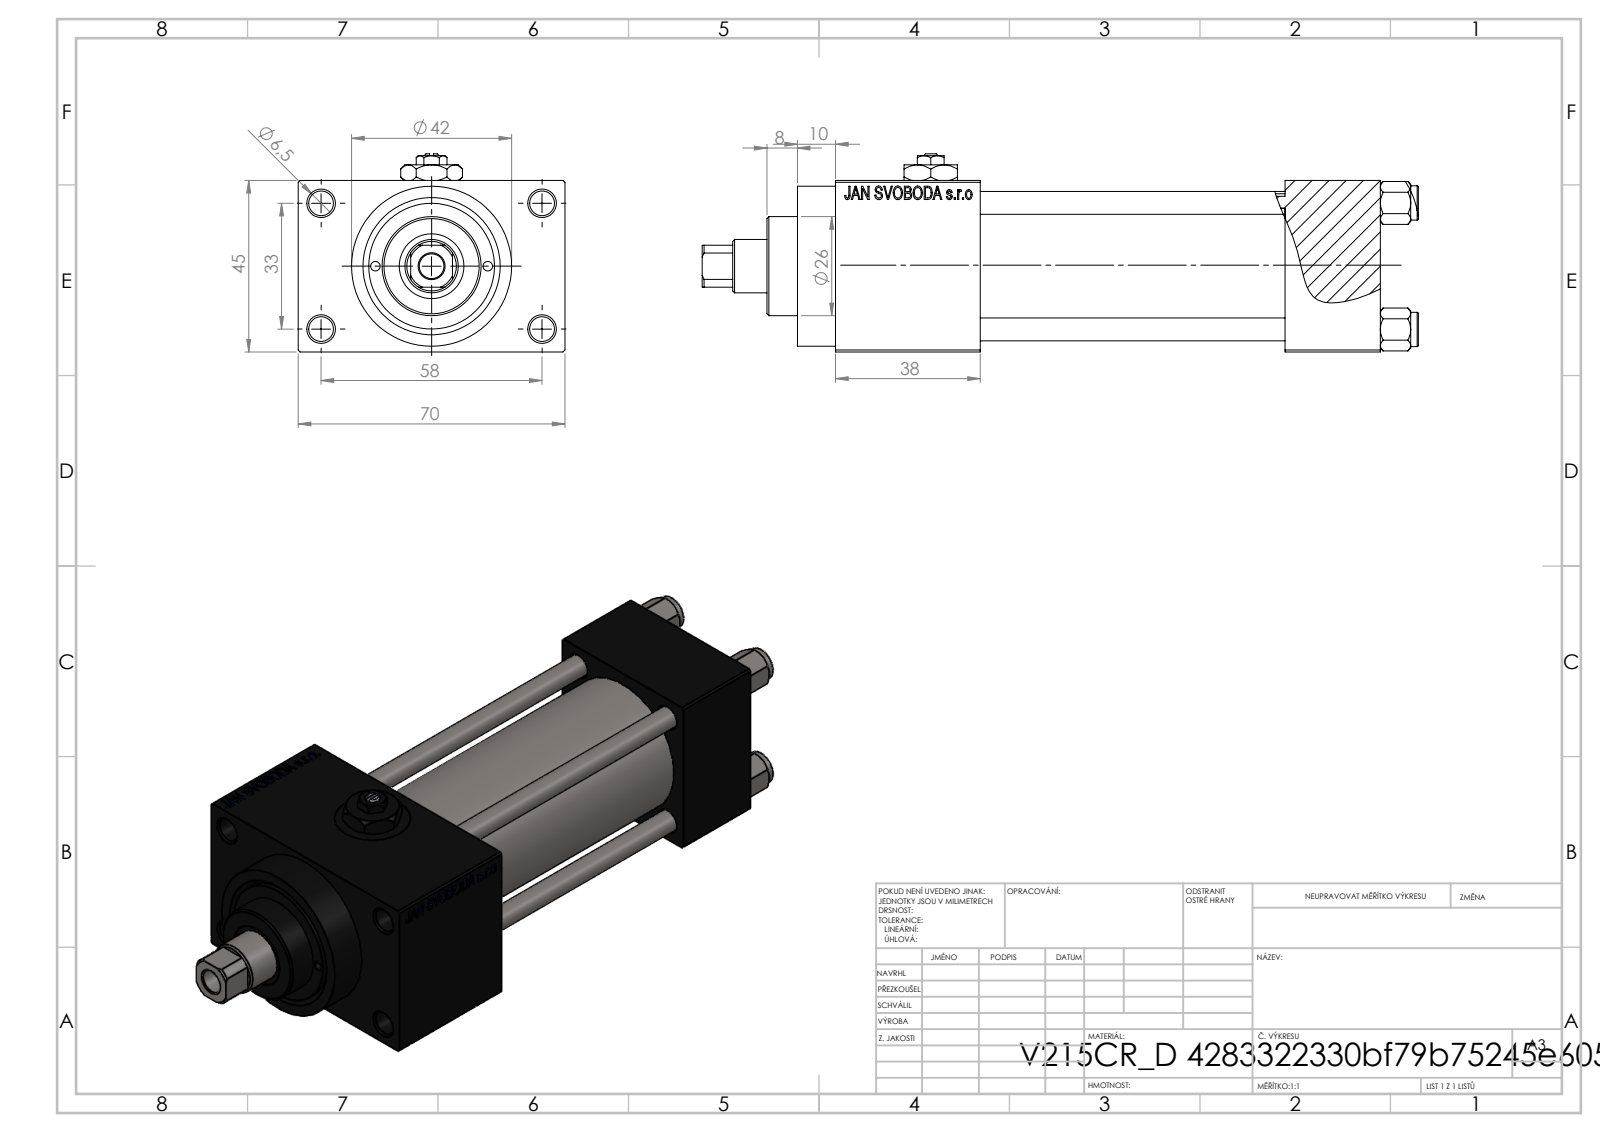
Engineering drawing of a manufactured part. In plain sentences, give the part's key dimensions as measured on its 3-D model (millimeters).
The part is named "NUT_M5_D; V215CR_VCP_D; Zatka_pro_OIL_PORT; V215CR_D_Body (+2 more)". Its 3-D file was written by "SolidWorks 2019 (CONFIG_CONTROL_DESIGN)". It is 12 solids with 1157 faces: 521 planar, 96 cylindrical and 540 other. Overall it measures 188 by 70 by 52 millimeters. Its volume is 247 987 cubic millimeters and its surface area 86 159 square millimeters. Round holes: 5 of diameter 6.5, 4 of diameter 6, 3 of diameter 13.16, 3 of diameter 20, 2 of diameter 2.5, 2 of diameter 7, 1 of diameter 14, 1 of diameter 17, 1 of diameter 24, 1 of diameter 32, 1 of diameter 33. Round bosses or shafts: 4 of diameter 9, 1 of diameter 42, 1 of diameter 38, 1 of diameter 26. Partial cylindrical surfaces (rounded edges, fillets, slot ends): 1 of radius 6.5. The main face-to-face distances are 45, 25, 12.5, 80, 105, 57.5, 118, 38, 143, 70. The hole center spacings are 12.4, 16.7, 21.8, 23.48, 33.2, 33.37, 35.35, 35.47.
